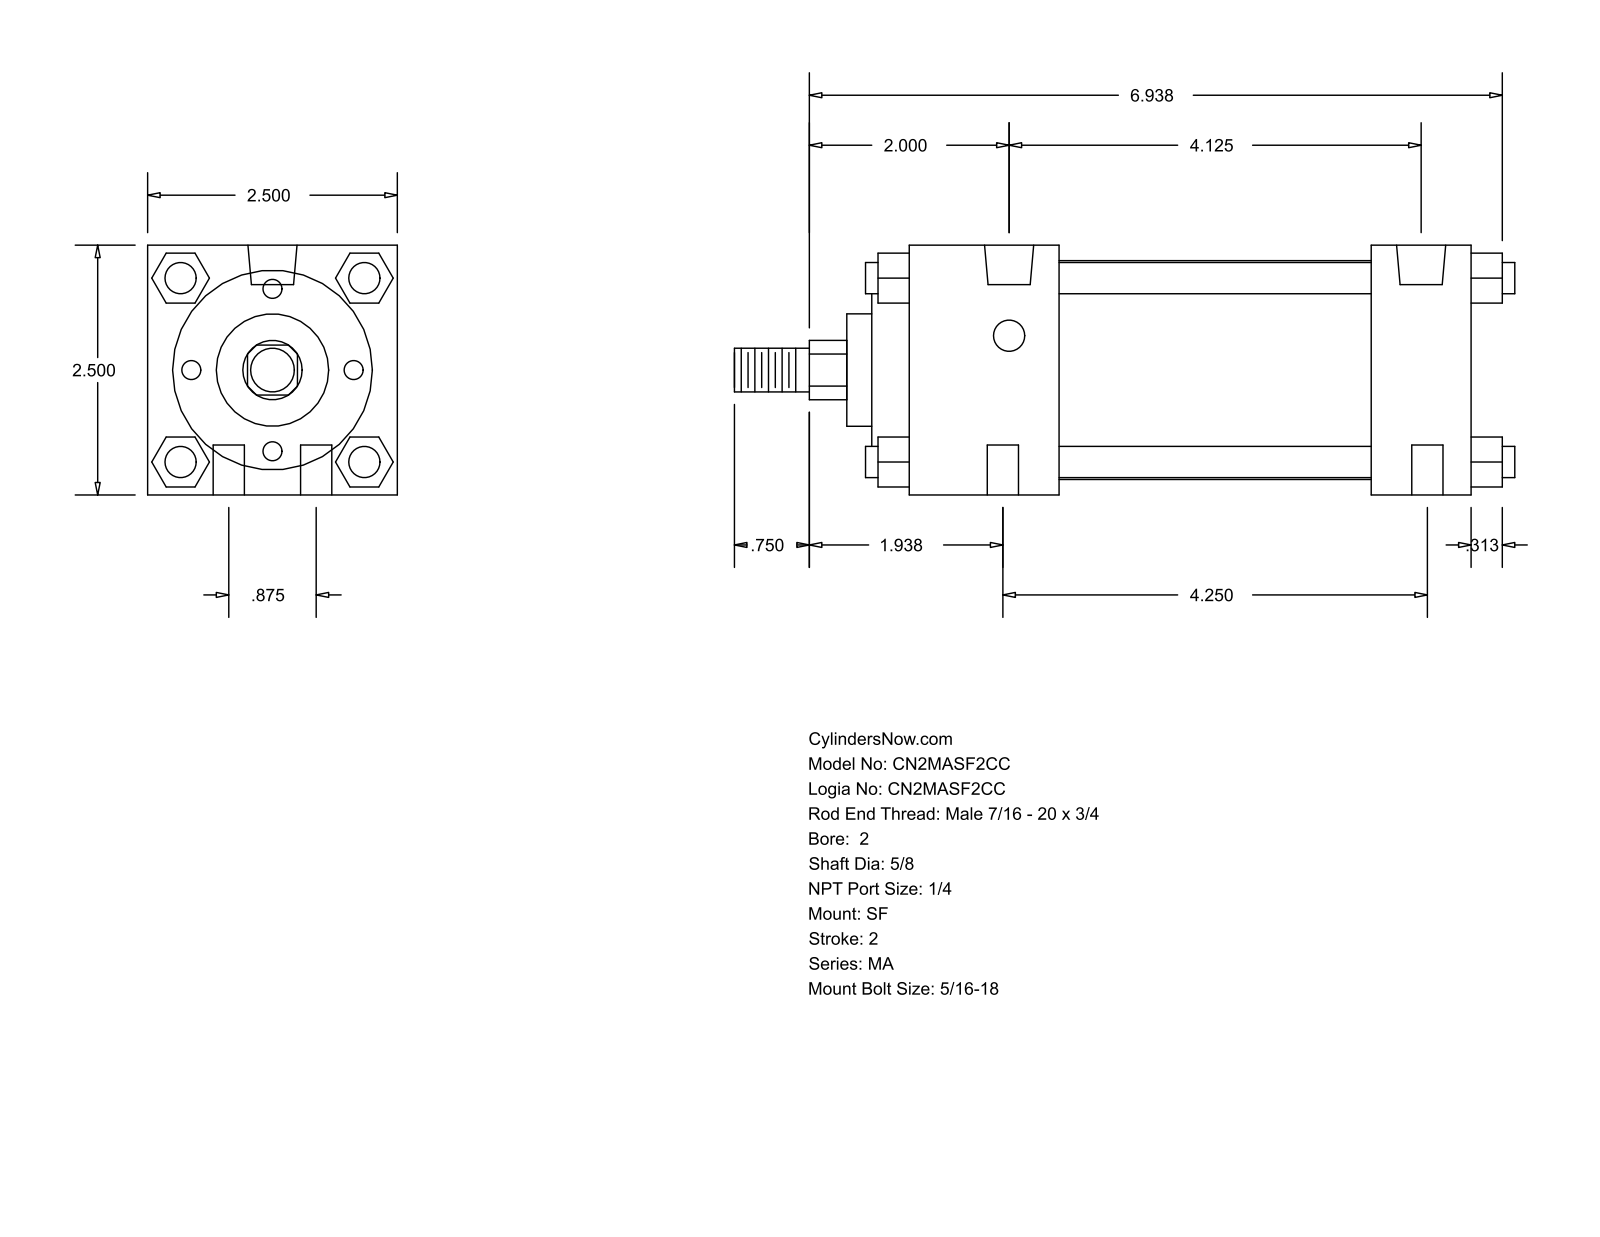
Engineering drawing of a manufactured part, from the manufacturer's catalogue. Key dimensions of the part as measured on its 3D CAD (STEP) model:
Part name (STEP PRODUCT): MA_SF__0200_0.625
STEP written by: GSSL Pune (CONFIG_CONTROL_DESIGN)
Units: millimetres
Bodies: 0 solids, 126 faces (95 planar, 31 cylindrical, 0 other)
Overall size (bounding box): 198.44 × 63.5 × 63.5
Round holes (diameter × count): ⌀7.94 ×6, ⌀12.49 ×2
Round bosses / shafts (diameter × count): ⌀7.94 ×4, ⌀55.63 ×1, ⌀50.8 ×1, ⌀28.57 ×1, ⌀15.88 ×1, ⌀11.11 ×1
Partial cylindrical surfaces — rounded edges, fillets, slot ends (radius × count): R7.54 ×1
Main face-to-face distances: 63.5, 25.4, 12.7, 38.1, 142.88, 117.48, 79.38, 104.78, 9.52, 47.62
Hole centre spacings: 11.22, 106.94, 22.22, 104.77, 107.95, 110.21
